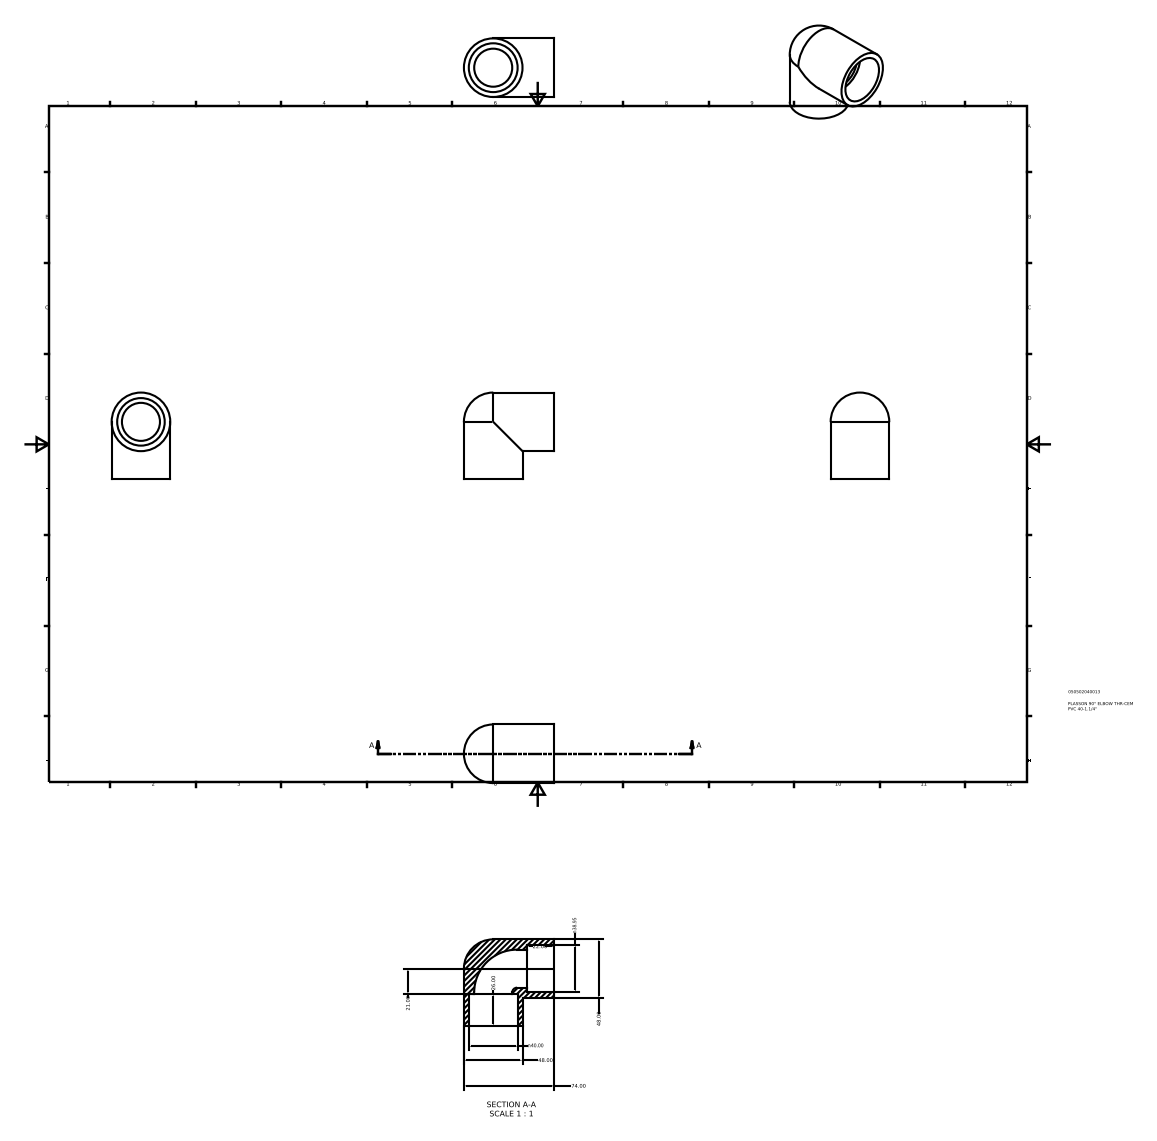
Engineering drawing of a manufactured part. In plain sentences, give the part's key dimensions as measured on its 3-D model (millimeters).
The part is named "050502040013". Its 3-D file was written by "Autodesk Inventor 2015 (AUTOMOTIVE_DESIGN)". It is 1 solid with 12 faces: 4 planar, 6 cylindrical and 2 other. Overall it measures 74 by 71 by 48 millimeters. Its volume is 81 688 cubic millimeters and its surface area 26 165 square millimeters. Round holes: 2 of diameter 31.16, 1 of diameter 38.95, 1 of diameter 40. Round bosses or shafts: 2 of diameter 48. The main face-to-face distances are 26, 22.
